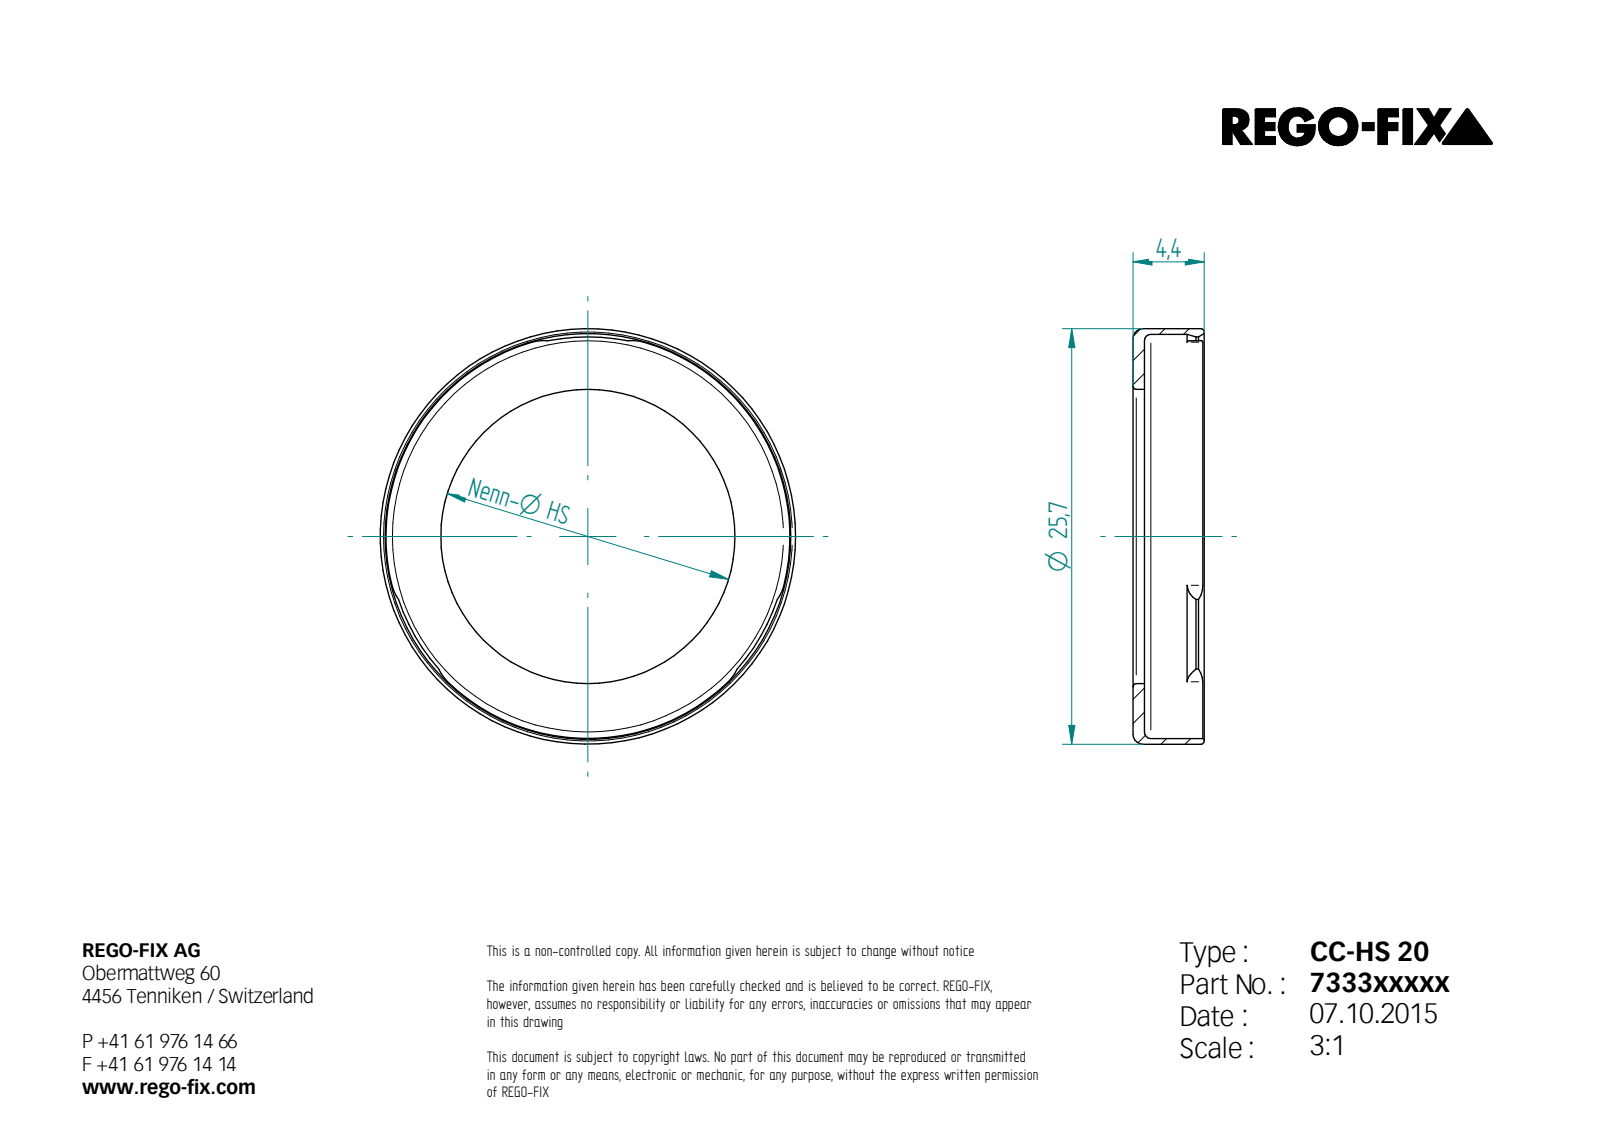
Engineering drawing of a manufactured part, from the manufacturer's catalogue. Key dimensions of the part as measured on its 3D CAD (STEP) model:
STEP written by: Unknown (AUTOMOTIVE_DESIGN)
Units: millimetres
Bodies: 1 solid, 23 faces (3 planar, 12 cylindrical, 8 other)
Overall size (bounding box): 25.7 × 25.7 × 4.4
Volume: 281 mm³ · Surface area: 1 155 mm²
Round holes (diameter × count): ⌀18.2 ×1, ⌀25 ×1
Round bosses / shafts (diameter × count): ⌀25.7 ×1
Partial cylindrical surfaces — rounded edges, fillets, slot ends (radius × count): R2.5 ×6, R12.35 ×1
Main face-to-face distances: 0.7, 4.4, 3.7
